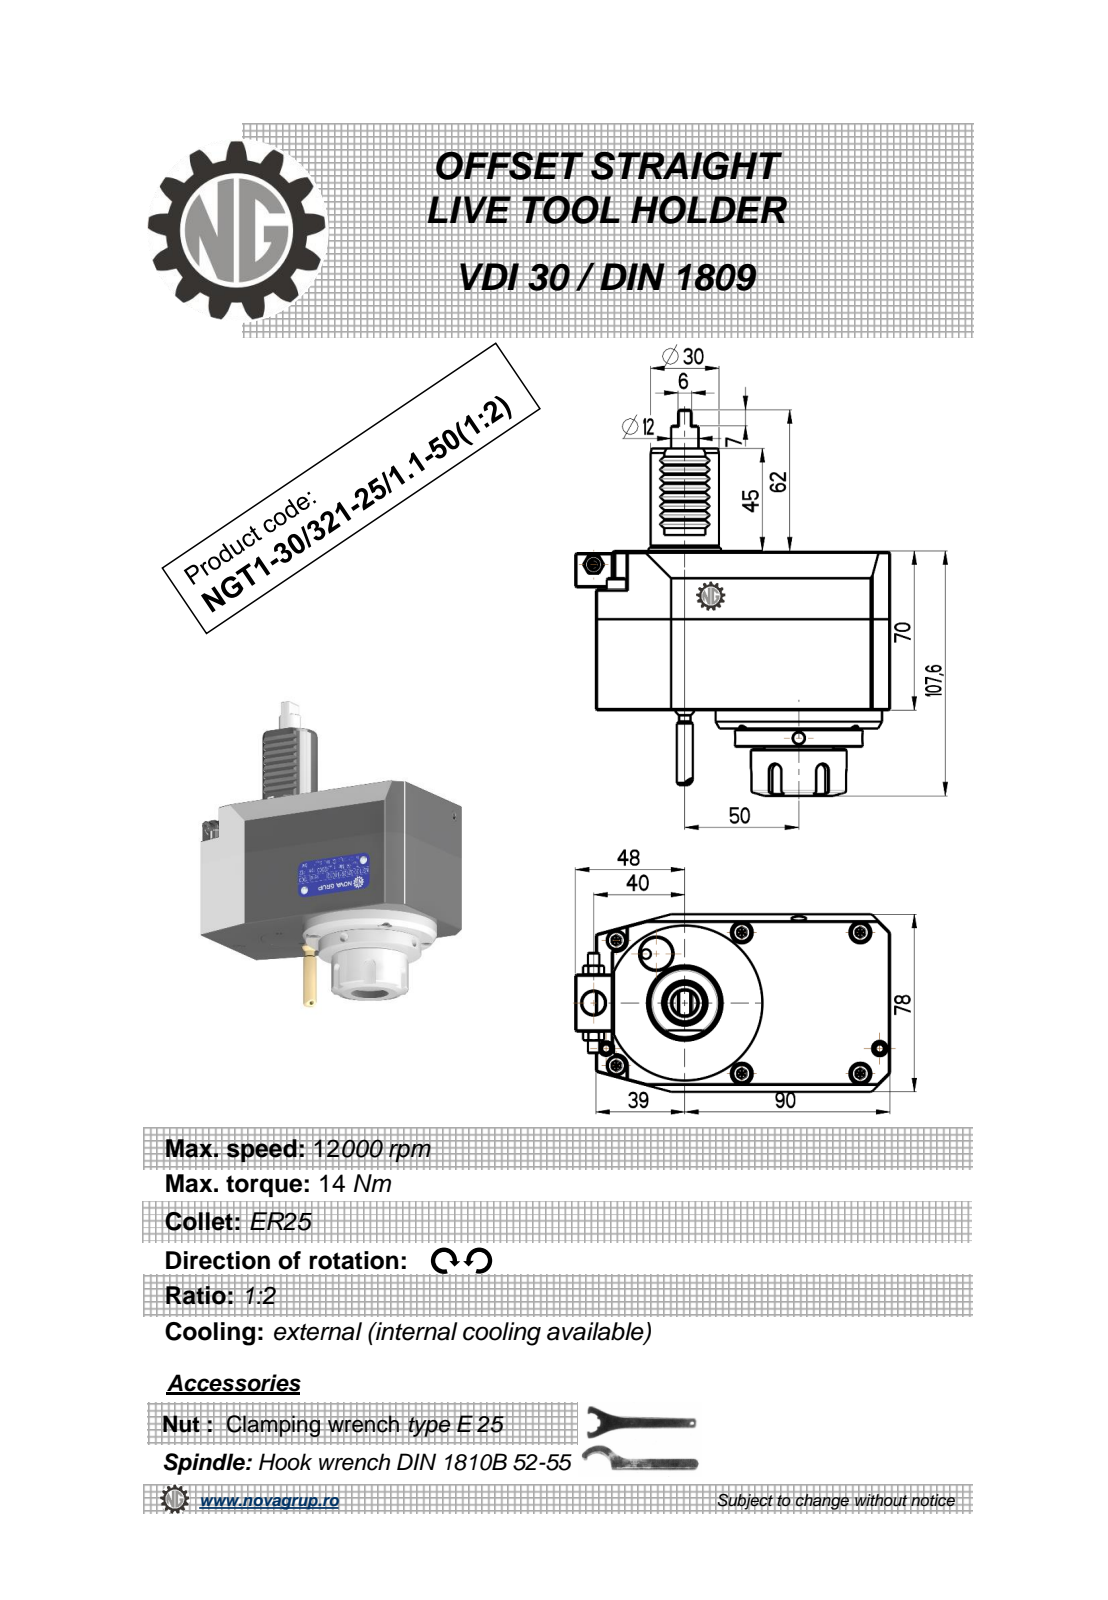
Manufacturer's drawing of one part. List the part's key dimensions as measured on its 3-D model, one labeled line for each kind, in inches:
Part name (STEP PRODUCT): NGT1_30_321_25_1_1_50_1_2
STEP written by: PRO/ENGINEER BY PARAMETRIC TECHNOLOGY CORPORATION, 2010280 (CONFIG_CONTROL_DESIGN)
Units: inches
Bodies: 1 solid, 380 faces (161 planar, 93 cylindrical, 126 other)
Overall size (bounding box): 6.677 × 5.433 × 3.071
Volume: 47.66 in³ · Surface area: 99.28 in²
Round holes (diameter × count): ⌀0.197 ×2, ⌀0.098 ×1, ⌀0.118 ×1, ⌀0.165 ×1, ⌀0.374 ×1, ⌀0.394 ×1, ⌀0.551 ×1
Round bosses / shafts (diameter × count): ⌀0.315 ×2, ⌀0.197 ×2, ⌀2.874 ×1, ⌀2.205 ×1, ⌀1.654 ×1, ⌀1.299 ×1, ⌀1.181 ×1, ⌀0.736 ×1
Partial cylindrical surfaces — rounded edges, fillets, slot ends (radius × count): R0.006 ×12, R0.01 ×12, R0.012 ×8, R0.118 ×5, R0.031 ×2, R0.177 ×2
Main face-to-face distances: 3.071, 2.756, 0.315, 5.079, 0.63, 3.386, 0.02, 2.717, 0.295, 3.091
Hole centre spacings: 0.492, 1.378, 1.788, 2.904, 4.644
